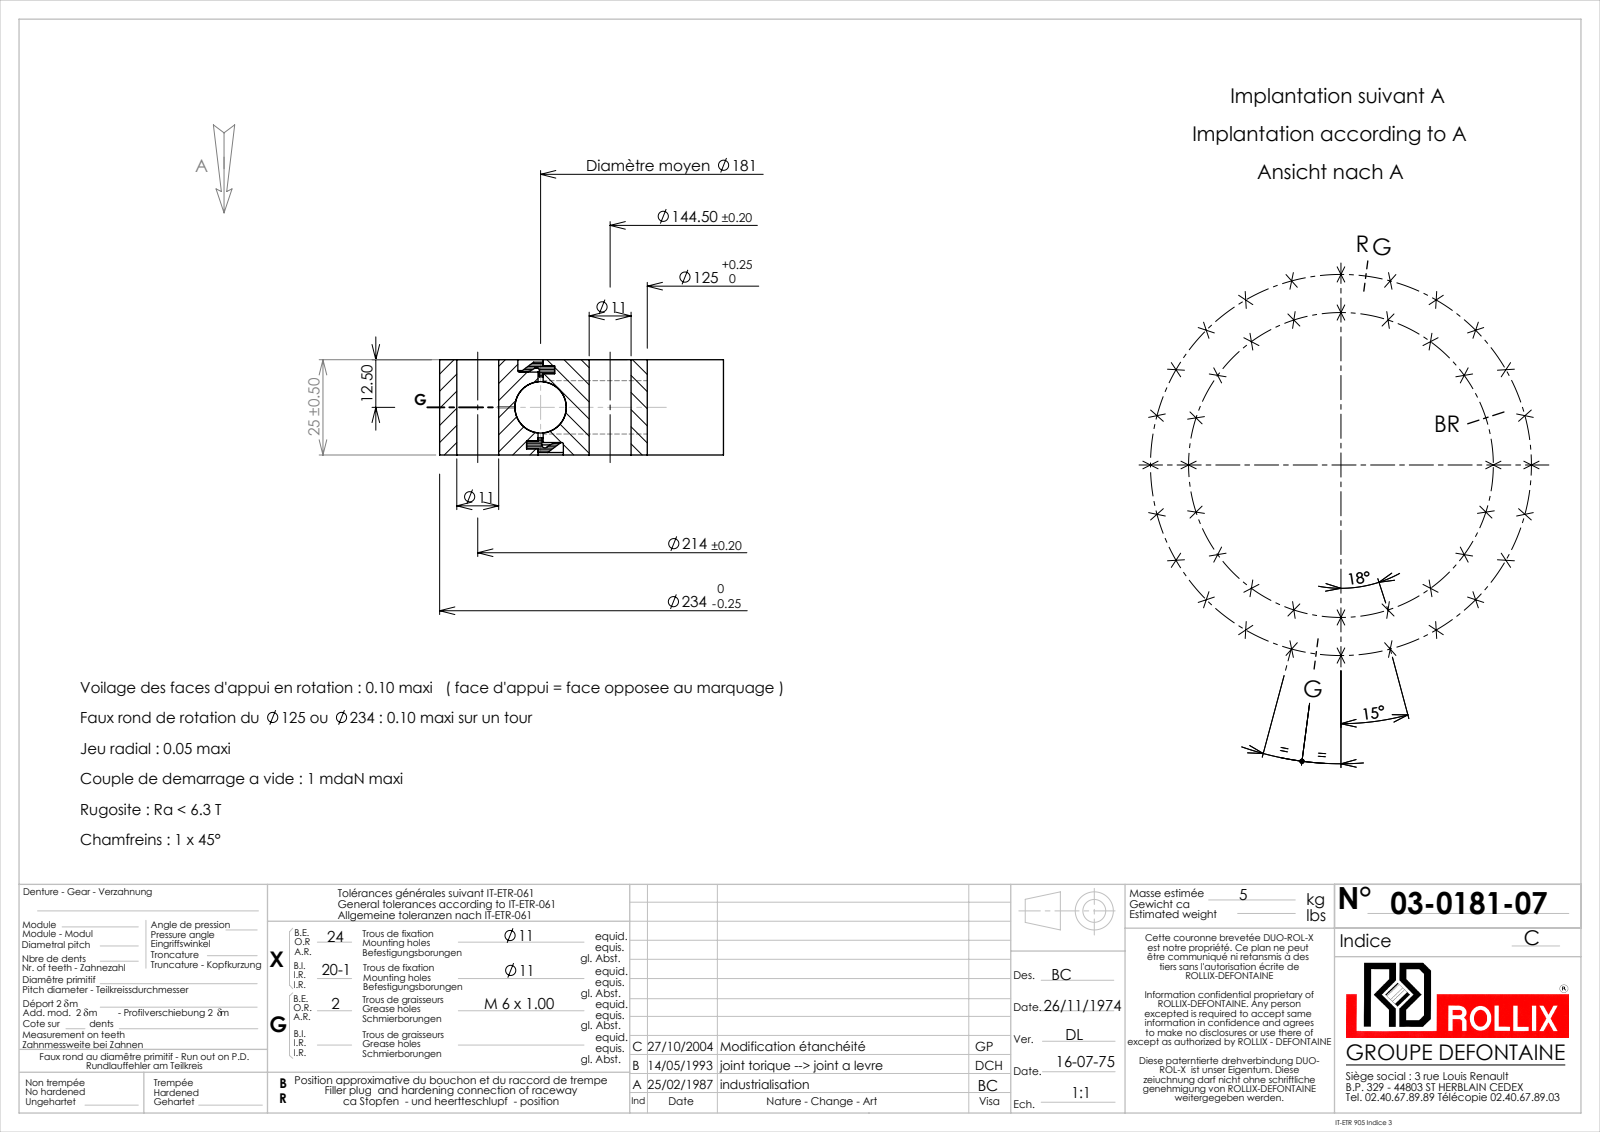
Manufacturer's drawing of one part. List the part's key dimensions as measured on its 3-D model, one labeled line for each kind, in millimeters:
Part name (STEP PRODUCT): 03-0181-07
STEP written by: SolidWorks 2016 (CONFIG_CONTROL_DESIGN)
Units: millimetres
Bodies: 5 solids, 174 faces (20 planar, 130 cylindrical, 24 other)
Overall size (bounding box): 234 × 234 × 25
Volume: 568 035 mm³ · Surface area: 189 270 mm²
Round holes (diameter × count): ⌀11 ×43, ⌀5 ×2, ⌀125 ×1, ⌀173.65 ×1, ⌀180.35 ×1, ⌀182.35 ×1, ⌀188.35 ×1, ⌀192.95 ×1
Round bosses / shafts (diameter × count): ⌀234 ×1, ⌀181.65 ×1, ⌀179.65 ×1, ⌀169.05 ×1
Main face-to-face distances: 25, 3.65, 21.35, 1.65, 23.35, 2, 19.7, 21.75, 3.25, 18.1
Hole centre spacings: 72.25, 116.9, 128.75, 142.72, 107, 137.43, 84.93, 102.18
